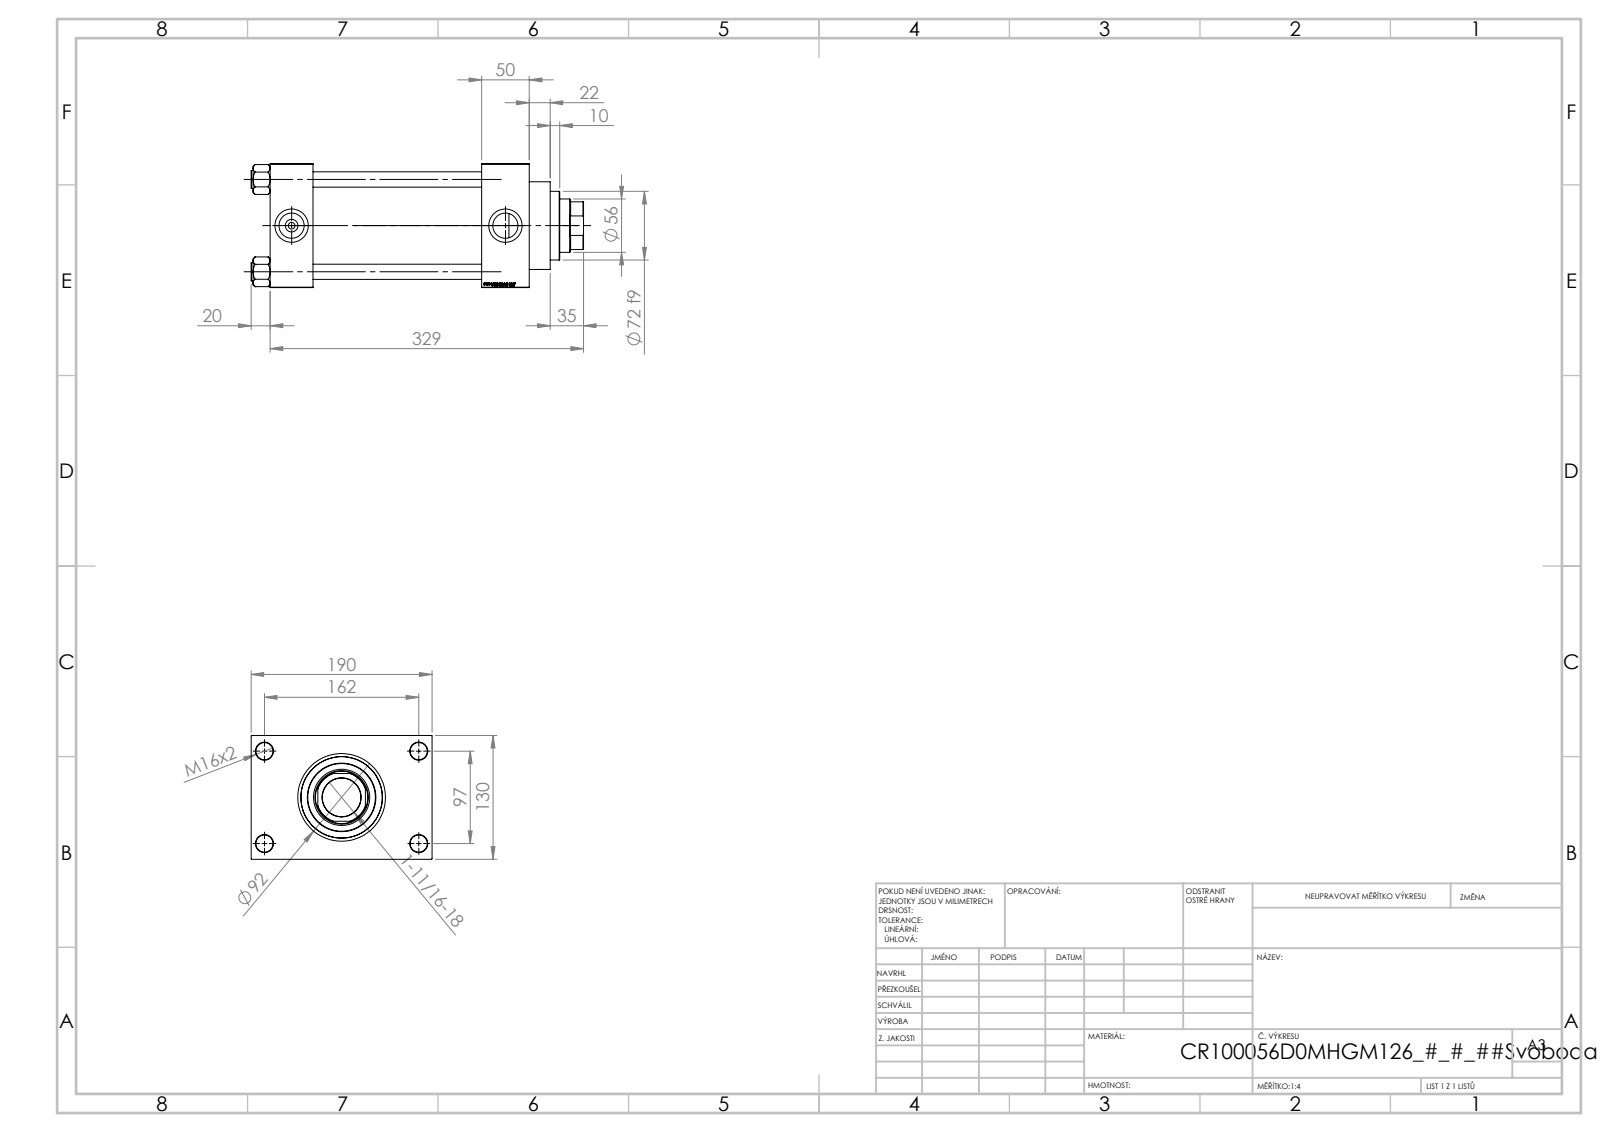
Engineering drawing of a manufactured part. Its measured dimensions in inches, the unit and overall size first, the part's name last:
Units: inches
Overall size (bounding box): 13.74 × 7.48 × 5.118
Round holes (diameter × count): ⌀0.63 ×4, ⌀0.709 ×4, ⌀0.276 ×2, ⌀1.041 ×2, ⌀1.378 ×2, ⌀1.594 ×1, ⌀2.205 ×1, ⌀2.323 ×1, ⌀2.992 ×1, ⌀3.366 ×1, ⌀3.937 ×1
Round bosses / shafts (diameter × count): ⌀0.748 ×4, ⌀4.173 ×1, ⌀3.622 ×1, ⌀2.835 ×1
Partial cylindrical surfaces — rounded edges, fillets, slot ends (radius × count): R1.063 ×1
Main face-to-face distances: 5.118, 1.969, 1.772, 8.74, 6.969, 10.709, 8.937, 1.181, 6.299, 7.48
Hole centre spacings: 1.281, 2.698, 3.717, 3.815, 4.026, 5.096, 6.367, 3.819
Volume: 187.8 in³ · Surface area: 729.9 in²
Bodies: 11 solids, 1151 faces (545 planar, 88 cylindrical, 518 other)
Part name (STEP PRODUCT): V215CR_VCP_D; V215CR_D_TYCINKA; V215_VC_A; V215CR_D_Body (+1 more)
STEP written by: SolidWorks 2019 (CONFIG_CONTROL_DESIGN)
